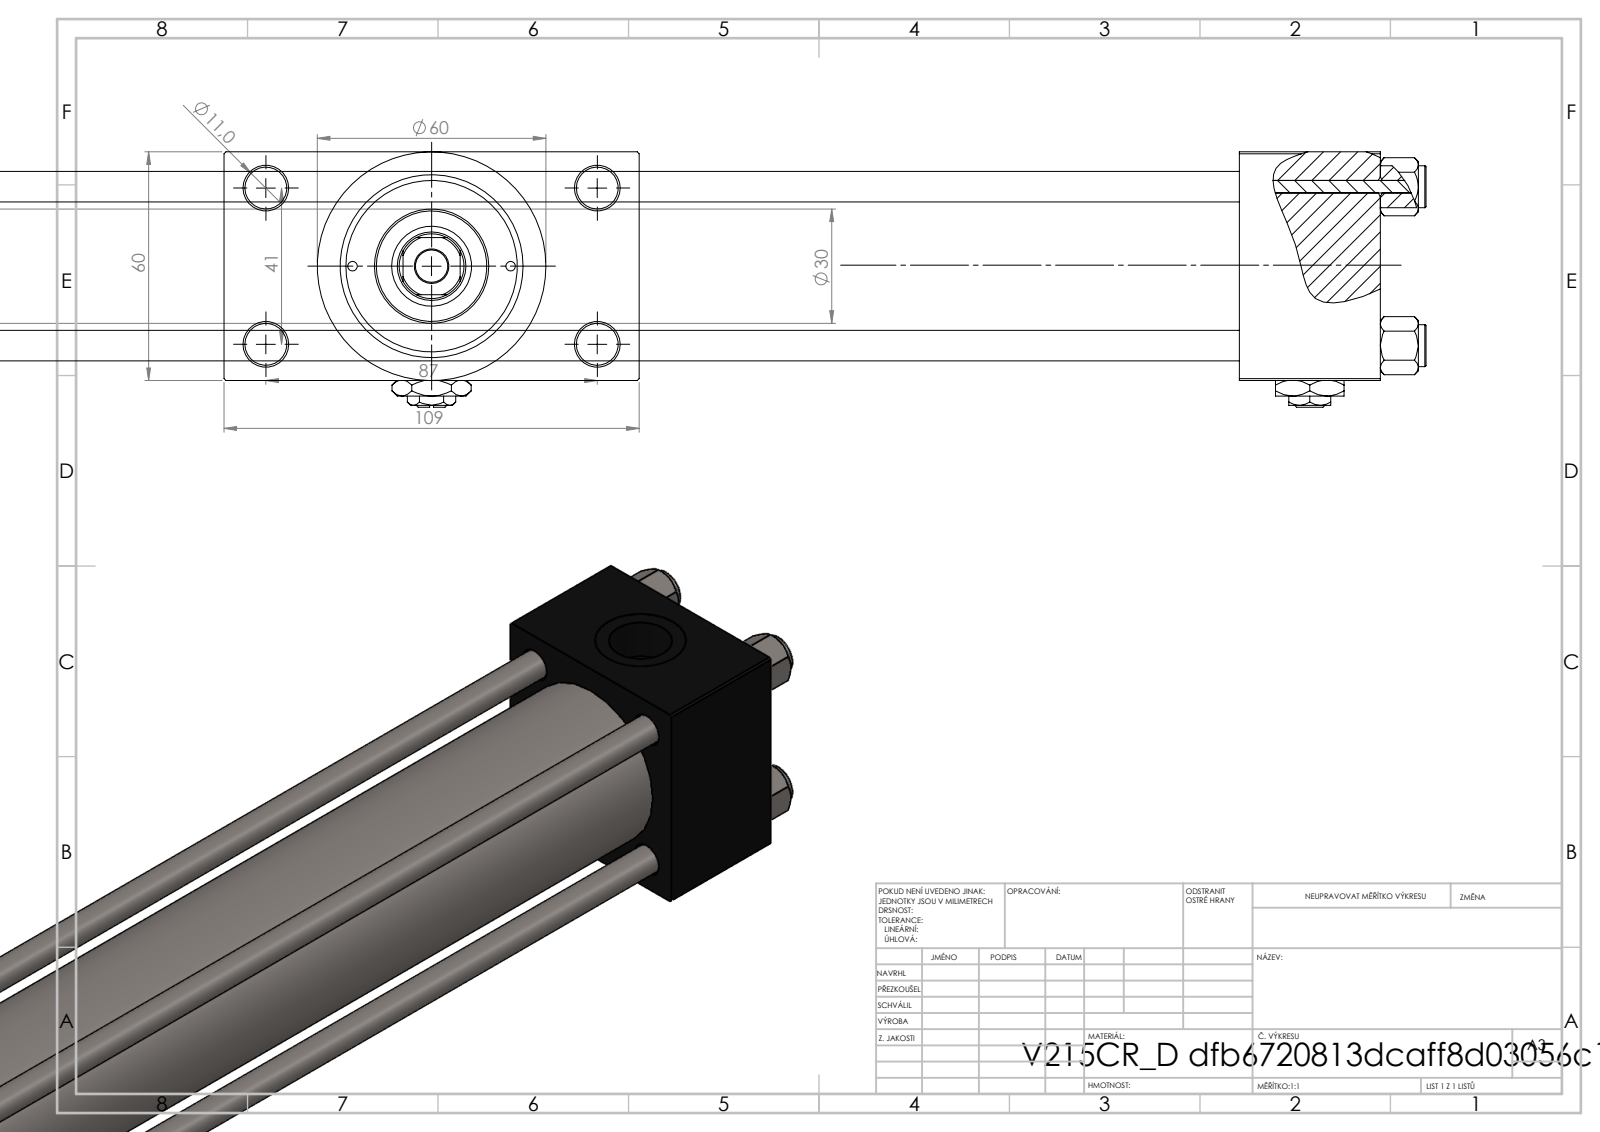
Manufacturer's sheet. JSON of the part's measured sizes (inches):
{"part_name": "V215CR_VCP_D; V215CR_D_Body; V215_VC_A; NUT_M5_D (+2 more)", "step_written_by": "SolidWorks 2019 (CONFIG_CONTROL_DESIGN)", "units": "inches", "bodies": {"solids": 13, "faces": 1214, "planar": 548, "cylindrical": 104, "other": 562}, "overall_size": [18.307, 4.291, 2.638], "volume_in3": 46.16, "surface_area_in2": 377.4, "round_holes": [[0.315, 4], [0.433, 4], [0.098, 2], [0.276, 2], [0.656, 2], [0.945, 2], [0.335, 1], [0.709, 1], [0.827, 1], [1.22, 1], [1.575, 1], [1.772, 1]], "round_bosses_or_shafts": [[0.433, 4], [2.362, 1], [1.811, 1], [1.181, 1]], "partial_cylinders_radius": [[0.335, 1]], "face_to_face_distances": [2.362, 0.965, 3.327, 13.307, 1.457, 14.764, 1.693, 16.457, 15, 4.291], "hole_center_spacings": [0.821, 0.892, 1.161, 1.206, 1.642, 1.832, 1.856, 1.893]}
